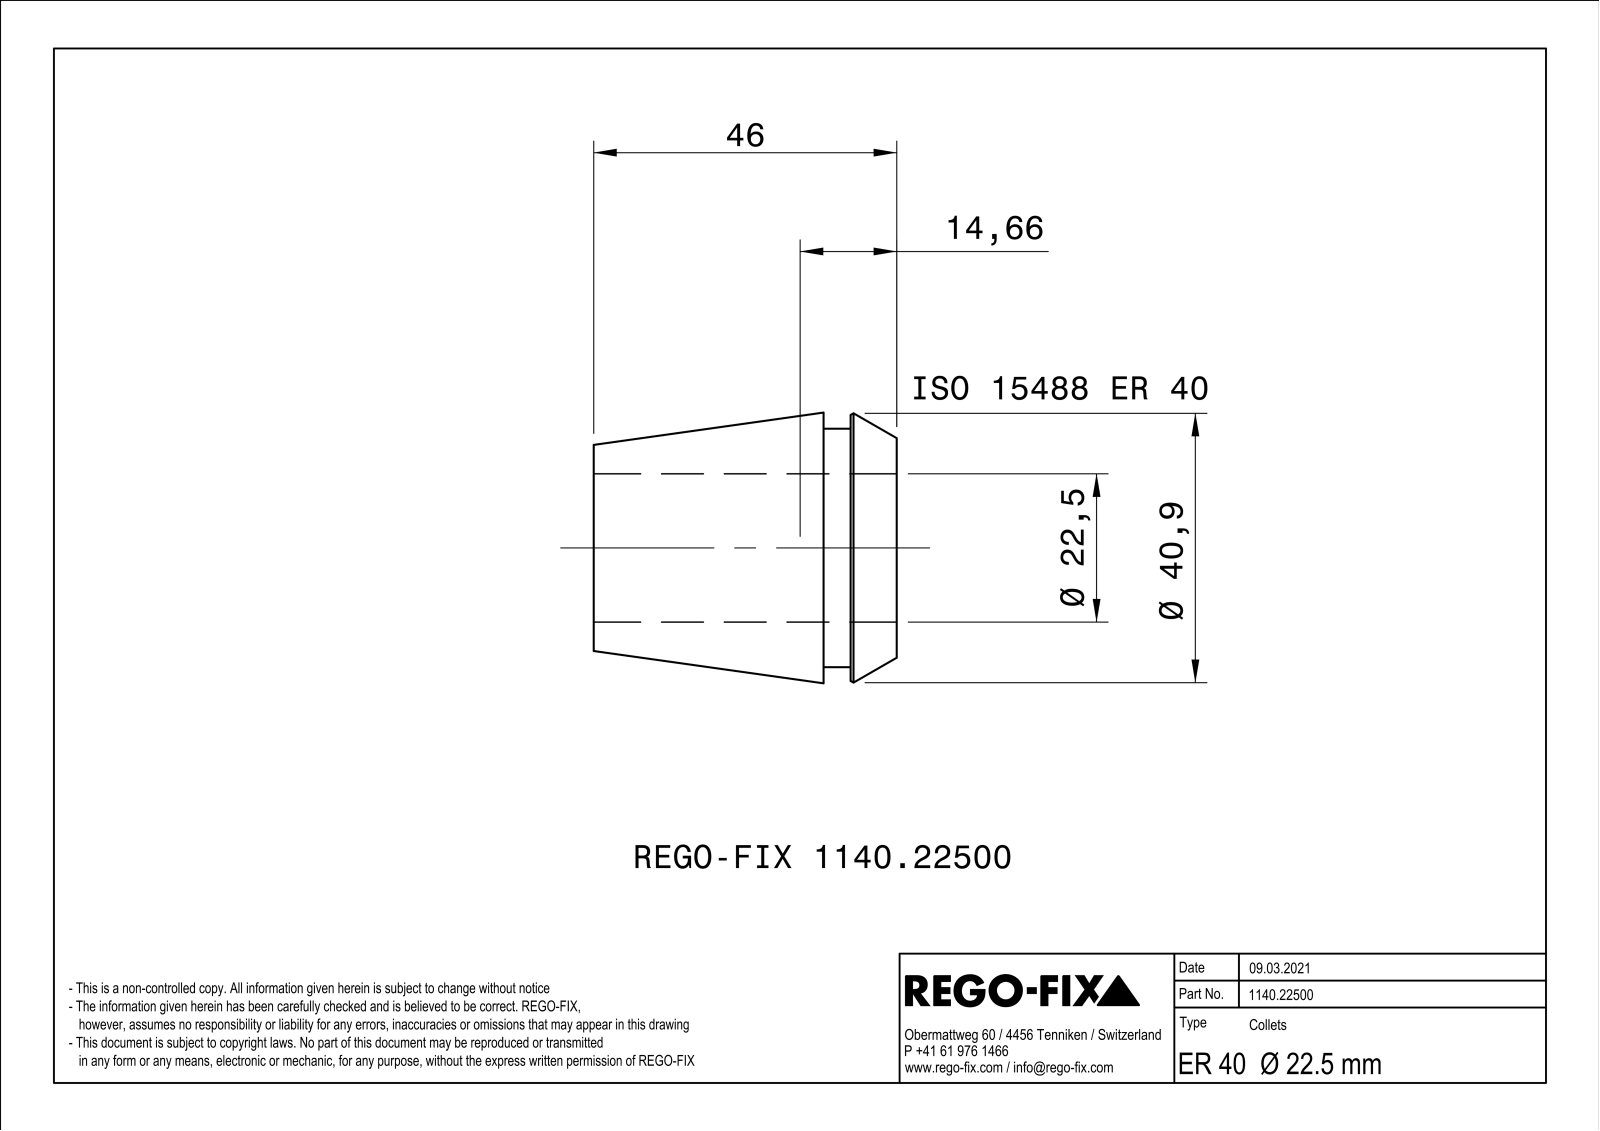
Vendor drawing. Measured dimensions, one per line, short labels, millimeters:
name: NOCUT
written by: SIEMENS PLM Software Solid Edge ST10 (AUTOMOTIVE_DESIGN)
unit: mm
bodies: 1 solid, 177 faces (88 planar, 9 cylindrical, 80 other)
size: 46 × 40.99 × 40.99
volume: 25 039 mm³; area: 17 653 mm²
holes: 1× ⌀22.5
bosses: 1× ⌀36.2
face distances: 1, 46, 11.1, 34.9, 7, 4.1, 39, 7.5, 0.5, 3.6
